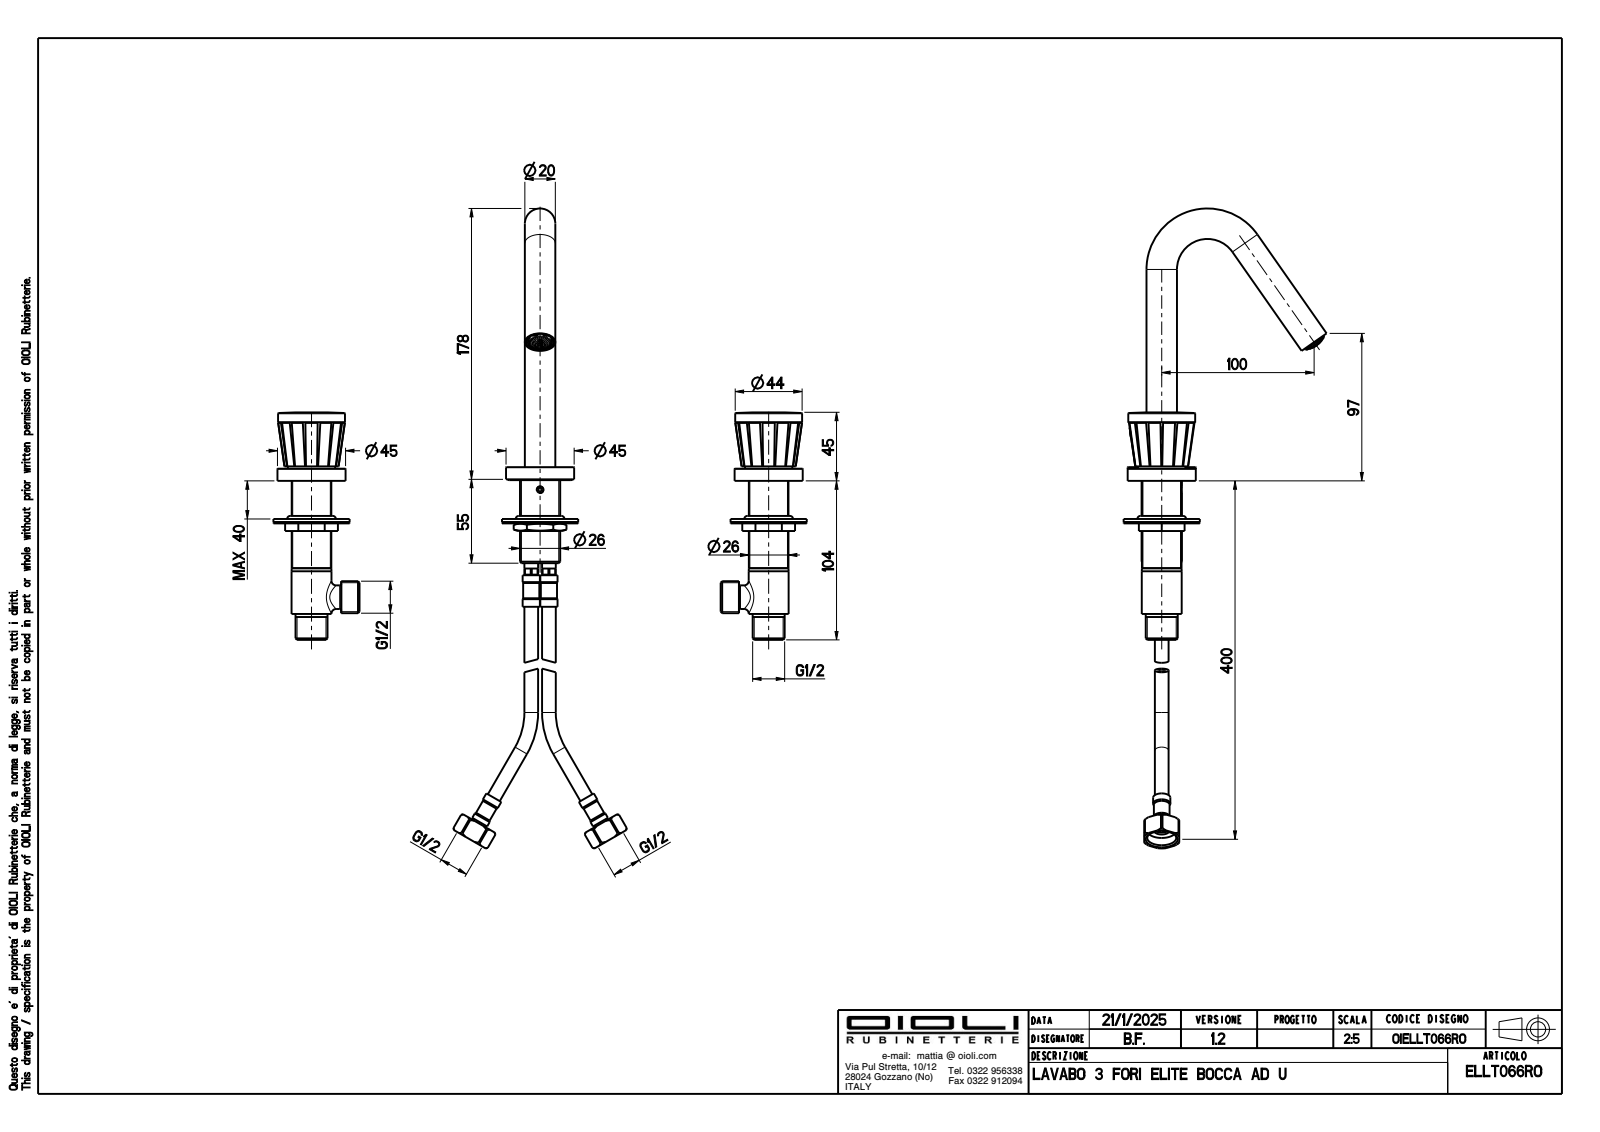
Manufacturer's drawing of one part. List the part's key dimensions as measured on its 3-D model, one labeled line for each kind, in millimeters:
Part name (STEP PRODUCT): OIBR00323; OICT00089; OIAR00087; OIVN00002 (+5 more)
STEP written by: CREO PARAMETRIC BY PTC INC, 2024493 (CONFIG_CONTROL_DESIGN)
Units: millimetres
Bodies: 15 solids, 1213 faces (522 planar, 481 cylindrical, 210 other)
Overall size (bounding box): 344.7 × 193.17 × 130.54
Volume: 113 666 mm³ · Surface area: 91 280 mm²
Round holes (diameter × count): ⌀0.6 ×81, ⌀4.2 ×4, ⌀17.5 ×3, ⌀42 ×3, ⌀3 ×2, ⌀4 ×2, ⌀5.3 ×2, ⌀6.5 ×2, ⌀7 ×2, ⌀11 ×2, ⌀17 ×2, ⌀17.3 ×2
Round bosses / shafts (diameter × count): ⌀44.7 ×3, ⌀36.5 ×3, ⌀18.5 ×3, ⌀43.9 ×2, ⌀31 ×2, ⌀26 ×2, ⌀24 ×2, ⌀21.1 ×2
Partial cylindrical surfaces — rounded edges, fillets, slot ends (radius × count): R0.1 ×18, R1 ×8, R0.2 ×4, R0.5 ×4, R1.2 ×4, R2 ×4, R3 ×4, R3.85 ×2
Main face-to-face distances: 8, 1, 9, 42, 34, 33, 7, 2.1, 5.9, 3.7
Hole centre spacings: 4.97, 3.31, 4.96, 1.65, 5.97, 1.3, 4.38, 1.66
